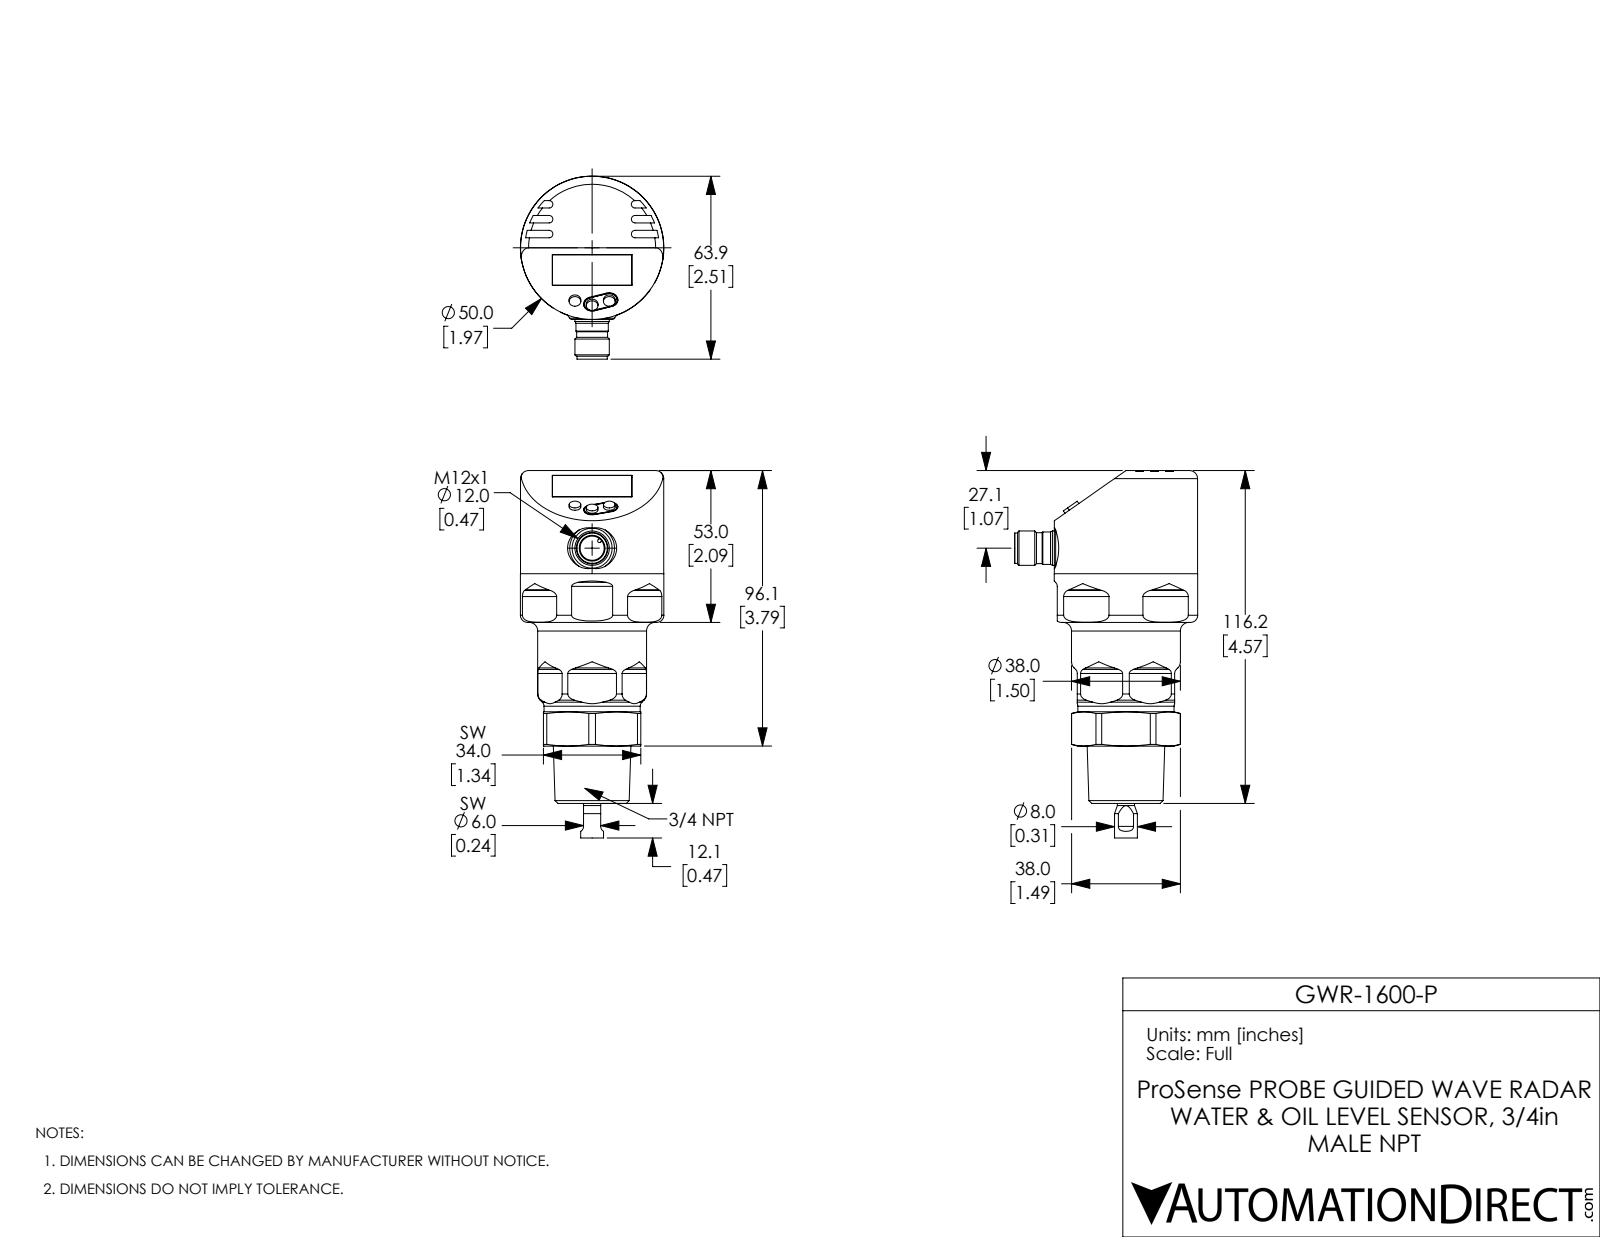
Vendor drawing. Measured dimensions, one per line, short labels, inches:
name: GWR-1600-P
written by: SolidWorks 2017 (AUTOMOTIVE_DESIGN)
unit: in
bodies: 1 solid, 204 faces (82 planar, 74 cylindrical, 48 other)
size: 5.049 × 2.516 × 1.972
volume: 9.332 in³; area: 29.47 in²
holes: 1× ⌀0.333
bosses: 3× ⌀0.161, 1× ⌀1.972, 1× ⌀1.969, 1× ⌀1.496, 1× ⌀1.323, 1× ⌀0.472, 1× ⌀0.445, 1× ⌀0.425
rounds: 16× R0.118, 9× R0.079, 6× R0.051, 2× R0.106, 1× R0.024
face distances: 1.339, 4.575, 0.787, 1.812, 3.787, 0.276, 1.614, 4.563, 3.776, 0.039
